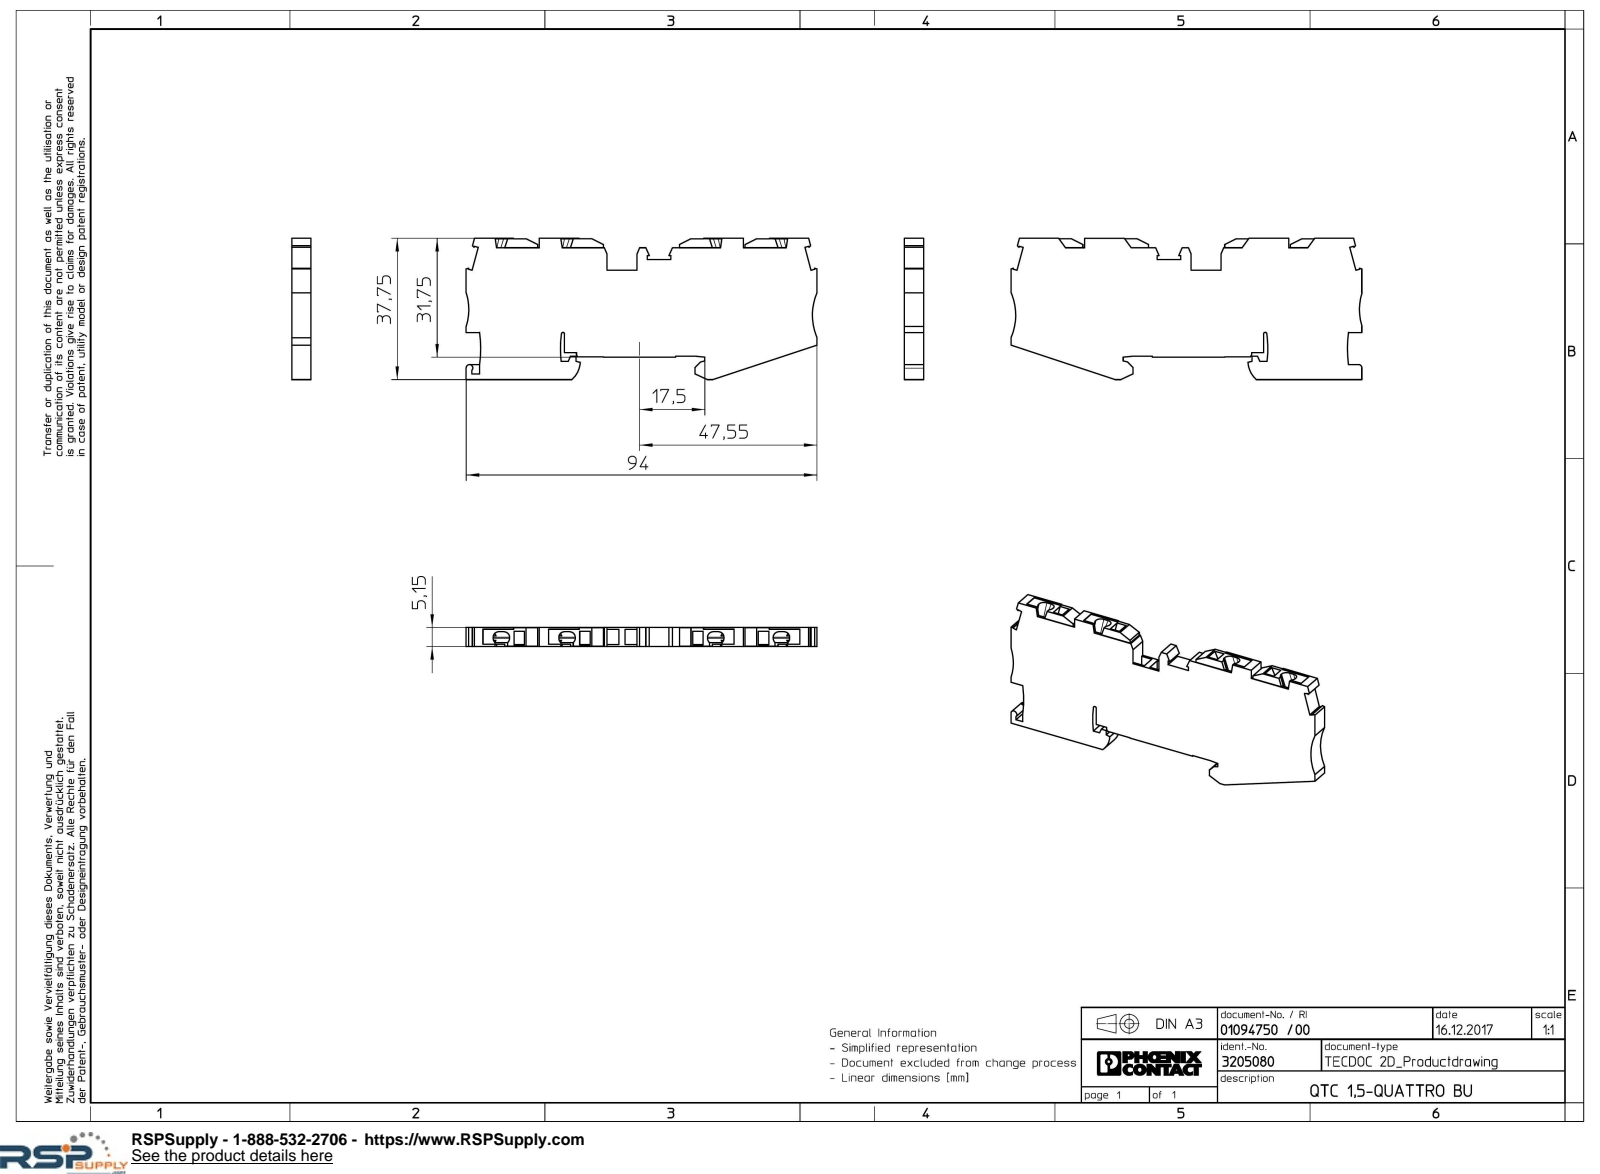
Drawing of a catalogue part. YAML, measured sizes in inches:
part_name: "QTC_1.5-QUATTRO_BU-select"
step_written_by: "Creo Elements/Direct Modeling 20.1A 29-Sep-2018 (C) Parametric Technology GmbH (AUTOMOTIVE_DESIGN)"
units: inches
bodies: {solids: 1, faces: 212, planar: 188, cylindrical: 24, other: 0}
overall_size: [3.701, 1.486, 0.203]
volume: 0.868
surface_area: 14.14
partial_cylinders:
  - {radius: 0.059, count: 16}
  - {radius: 0.016, count: 2}
  - {radius: 0.591, count: 2}
  - {radius: 1.248, count: 2}
  - {radius: 0.035, count: 1}
  - {radius: 0.26, count: 1}
face_to_face_distances: [0.203, 0.157, 0.019, 1.246, 1.486, 0.02, 0.236, 0.048, 0.094, 0.199]
